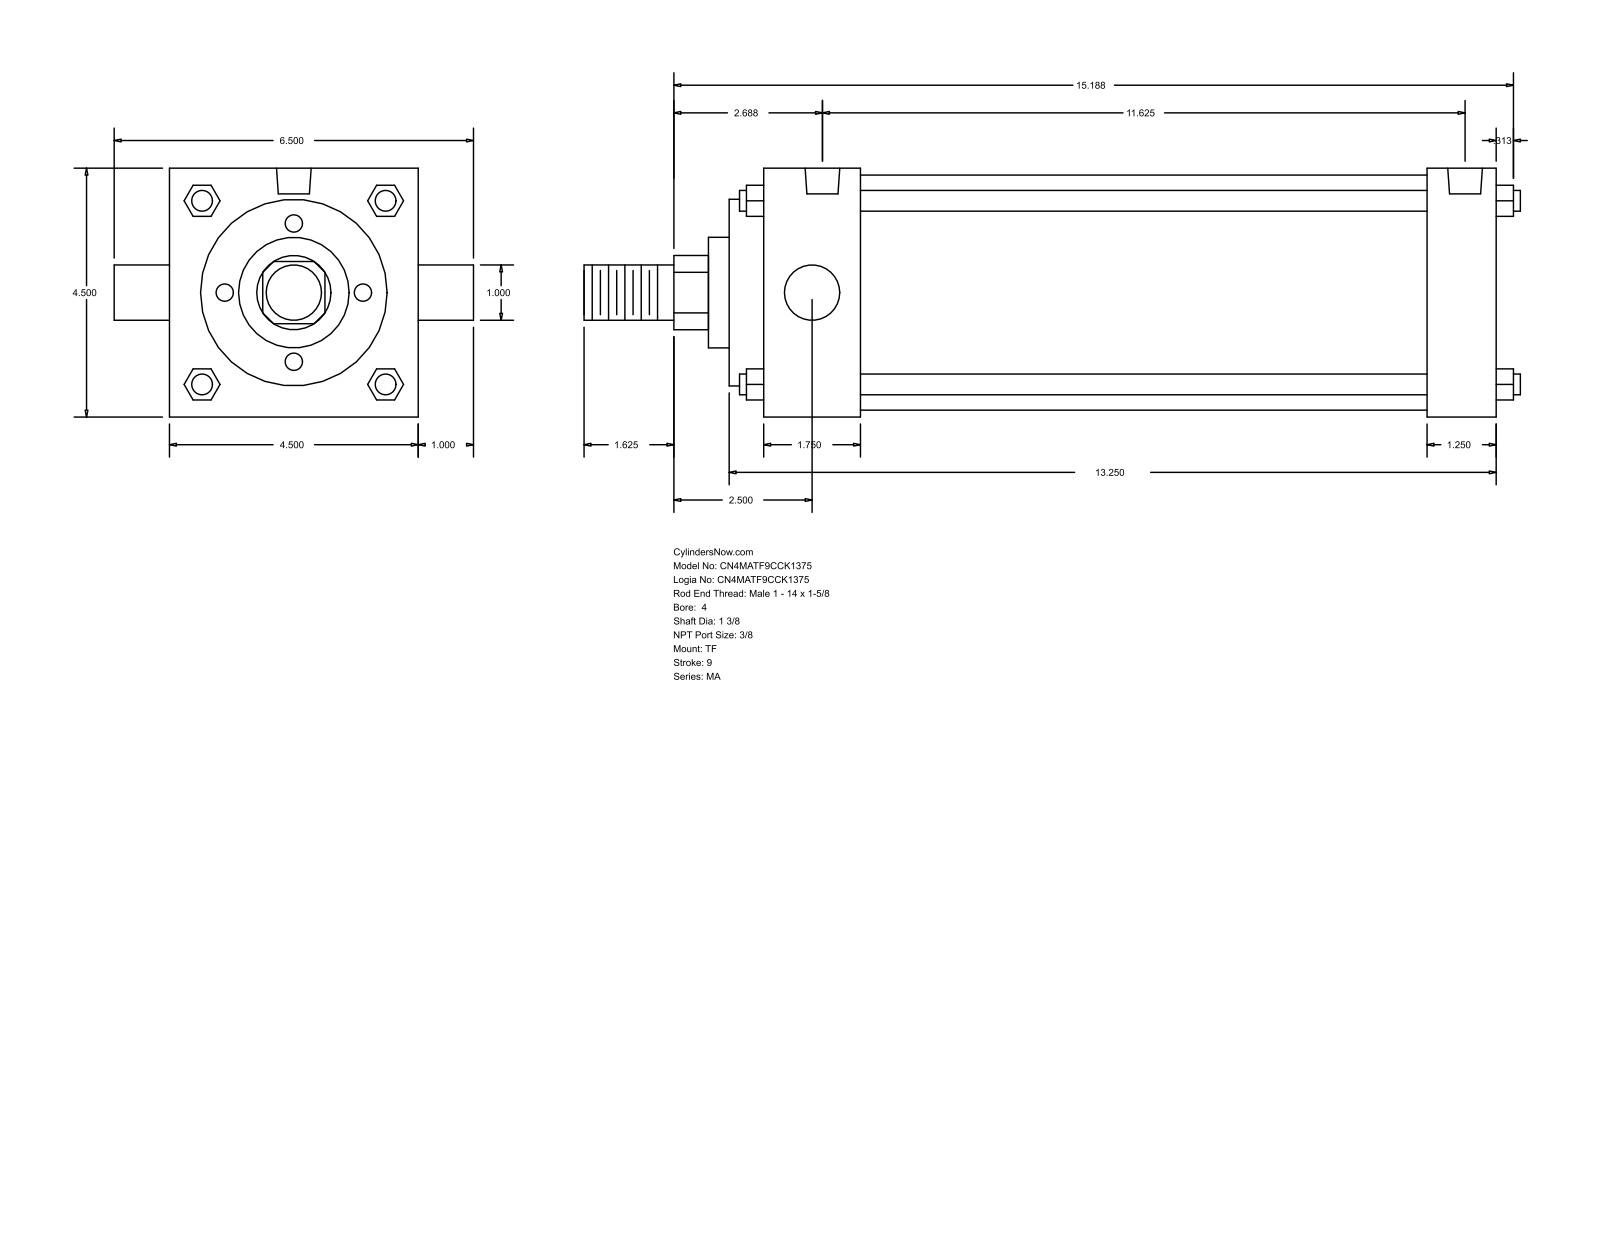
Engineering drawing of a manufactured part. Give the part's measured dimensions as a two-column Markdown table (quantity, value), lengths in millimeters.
| quantity | value |
| --- | --- |
| part name | MA_TF__0400_1.375 |
| STEP written by | GSSL Pune (CONFIG_CONTROL_DESIGN) |
| units | millimeters |
| bodies | 0 solids, 122 faces (93 planar, 29 cylindrical, 0 other) |
| overall size | 430.21 × 165.1 × 114.3 |
| round holes (diameter × count) | 11.11 × 3, 15.93 × 2 |
| round bosses / shafts (diameter × count) | 9.53 × 4, 25.4 × 2, 107.95 × 1, 85.72 × 1, 50.8 × 1, 34.92 × 1 |
| partial cylindrical surfaces (radius × count) | 17.06 × 1 |
| main face-to-face distances | 114.3, 336.55, 352.42, 15.87, 320.67, 304.8, 31.75, 60.32, 44.45, 260.35 |
| hole center spacings | 4.77, 290.51, 285.74, 295.28 |
